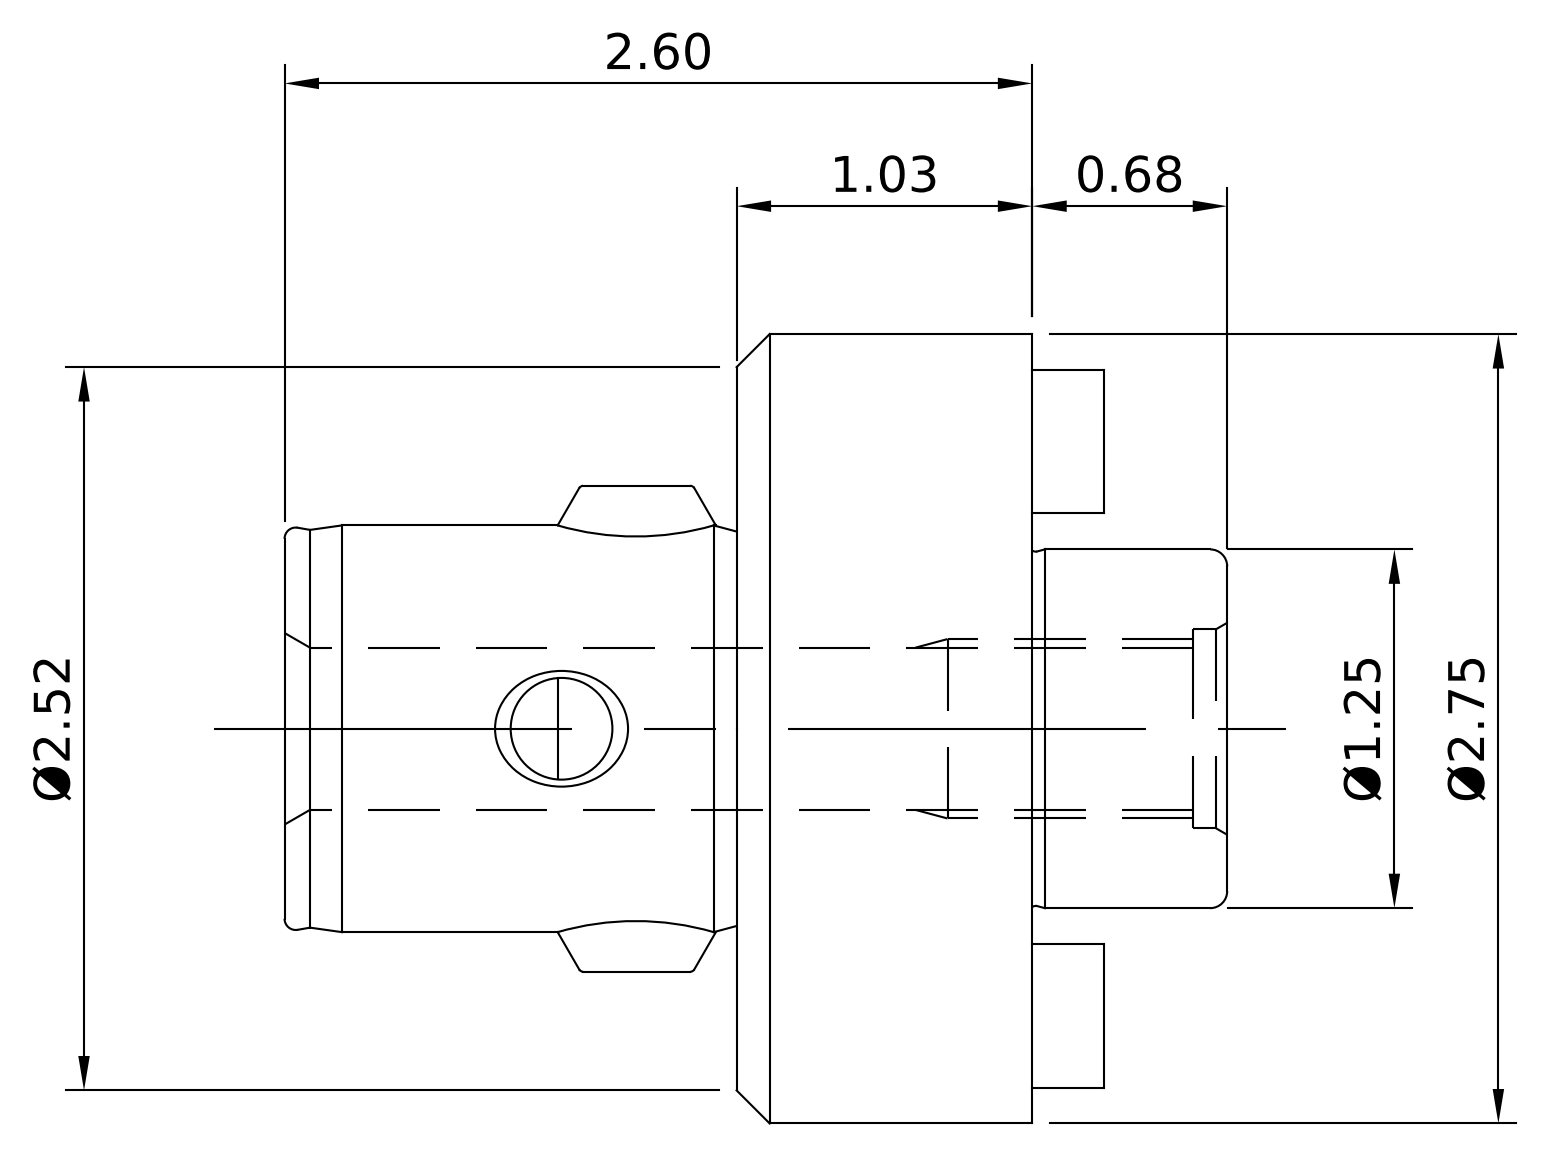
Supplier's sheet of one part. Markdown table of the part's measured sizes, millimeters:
| quantity | value |
| --- | --- |
| part name | 11.335.404; 10.691.50X_10.691.506; 691-50XRing_10.691.506Ring; 11.690.712 (+1 more) |
| STEP written by | SolidWorks 2016 (CONFIG_CONTROL_DESIGN) |
| units | millimeters |
| bodies | 6 solids, 268 faces (56 planar, 83 cylindrical, 129 other) |
| overall size | 97.36 × 69.85 × 69.85 |
| volume | 158 600 mm³ |
| surface area | 34 815 mm² |
| round holes (diameter × count) | 12.7 × 2, 8.03 × 1, 9 × 1, 14 × 1, 14.68 × 1, 16 × 1, 17.6 × 1, 18.5 × 1 |
| round bosses / shafts (diameter × count) | 12.71 × 2, 12.69 × 2, 69.85 × 1, 38.1 × 1, 36 × 1, 31.75 × 1, 15.87 × 1, 13.9 × 1 |
| partial cylindrical surfaces (radius × count) | 18 × 1 |
| main face-to-face distances | 26.16, 12.7, 57.36, 31.2, 44.66, 18.5, 40, 66.16, 84.66, 97.36 |
| hole center spacings | 25.4, 50.8 |
